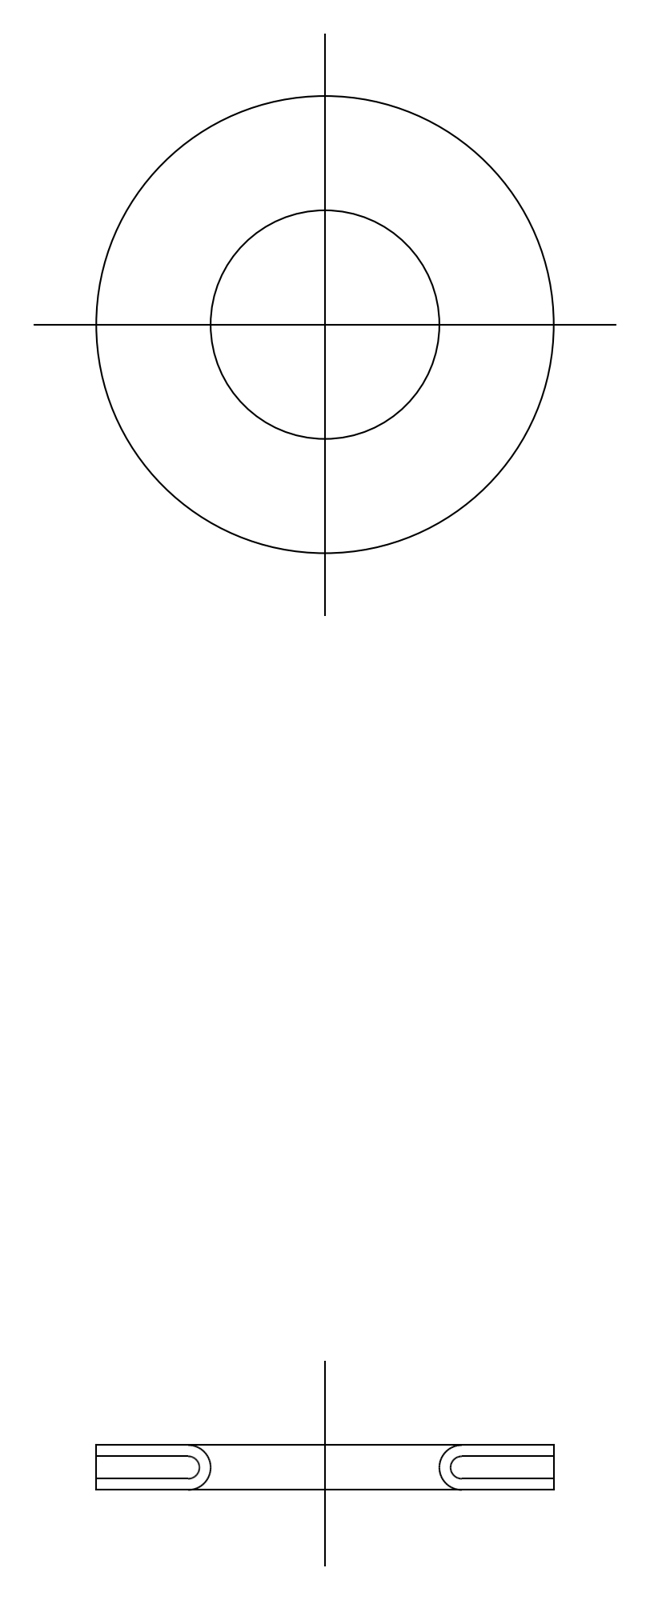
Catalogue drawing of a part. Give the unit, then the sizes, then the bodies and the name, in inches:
Units: inches
Overall size (bounding box): 0.803 × 0.803 × 0.079
Volume: 0.015 in³ · Surface area: 1.657 in²
Bodies: 1 solid, 12 faces (0 planar, 0 cylindrical, 12 other)
Part name (STEP PRODUCT): grommet
STEP written by: CADfix (AUTOMOTIVE_DESIGN)
